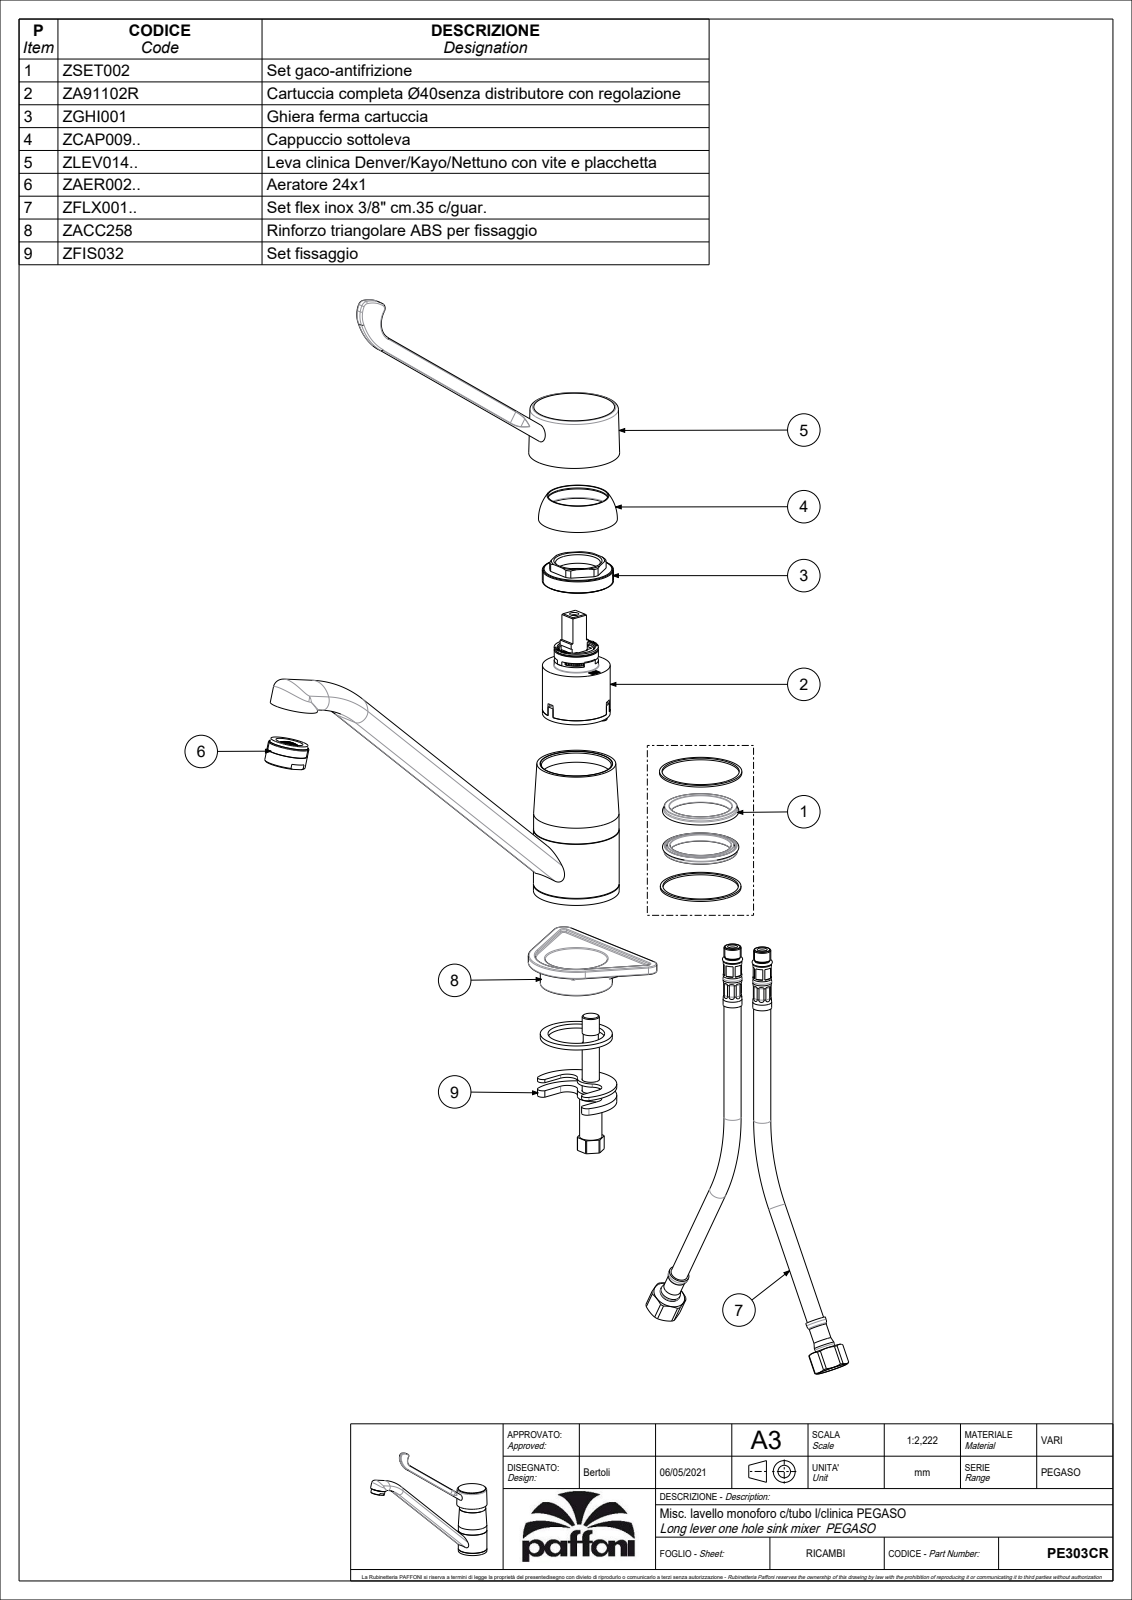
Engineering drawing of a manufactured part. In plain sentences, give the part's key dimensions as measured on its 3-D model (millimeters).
The part is named "PE303CR_SW0001". Its 3-D file was written by "CREO PARAMETRIC BY PTC INC, 2022124 (CONFIG_CONTROL_DESIGN)". It is 2 solids with 191 faces: 51 planar, 74 cylindrical and 66 other. Overall it measures 253.52 by 218.78 by 53 millimeters. Its volume is 309 546 cubic millimeters and its surface area 60 322 square millimeters. Round holes: 3 of diameter 9, 1 of diameter 11, 1 of diameter 11.6, 1 of diameter 44, 1 of diameter 47.5, 1 of diameter 48.2. Round bosses or shafts: 1 of diameter 50, 1 of diameter 49.8, 1 of diameter 47.85, 1 of diameter 46.5, 1 of diameter 44.8, 1 of diameter 43.7, 1 of diameter 40.5, 1 of diameter 37. Partial cylindrical surfaces (rounded edges, fillets, slot ends): 4 of radius 0.3, 4 of radius 5.5, 2 of radius 16.5, 2 of radius 18.3, 2 of radius 25.63, 1 of radius 3.5, 1 of radius 3.6, 1 of radius 11.17. The main face-to-face distances are 4.5, 7.5, 19.5, 2.5, 17, 87.2, 18.4, 27.9, 9.5, 68.8. The hole center spacings are 0.4, 0.5, 1, 1.5, 6, 6.5, 7.5.
